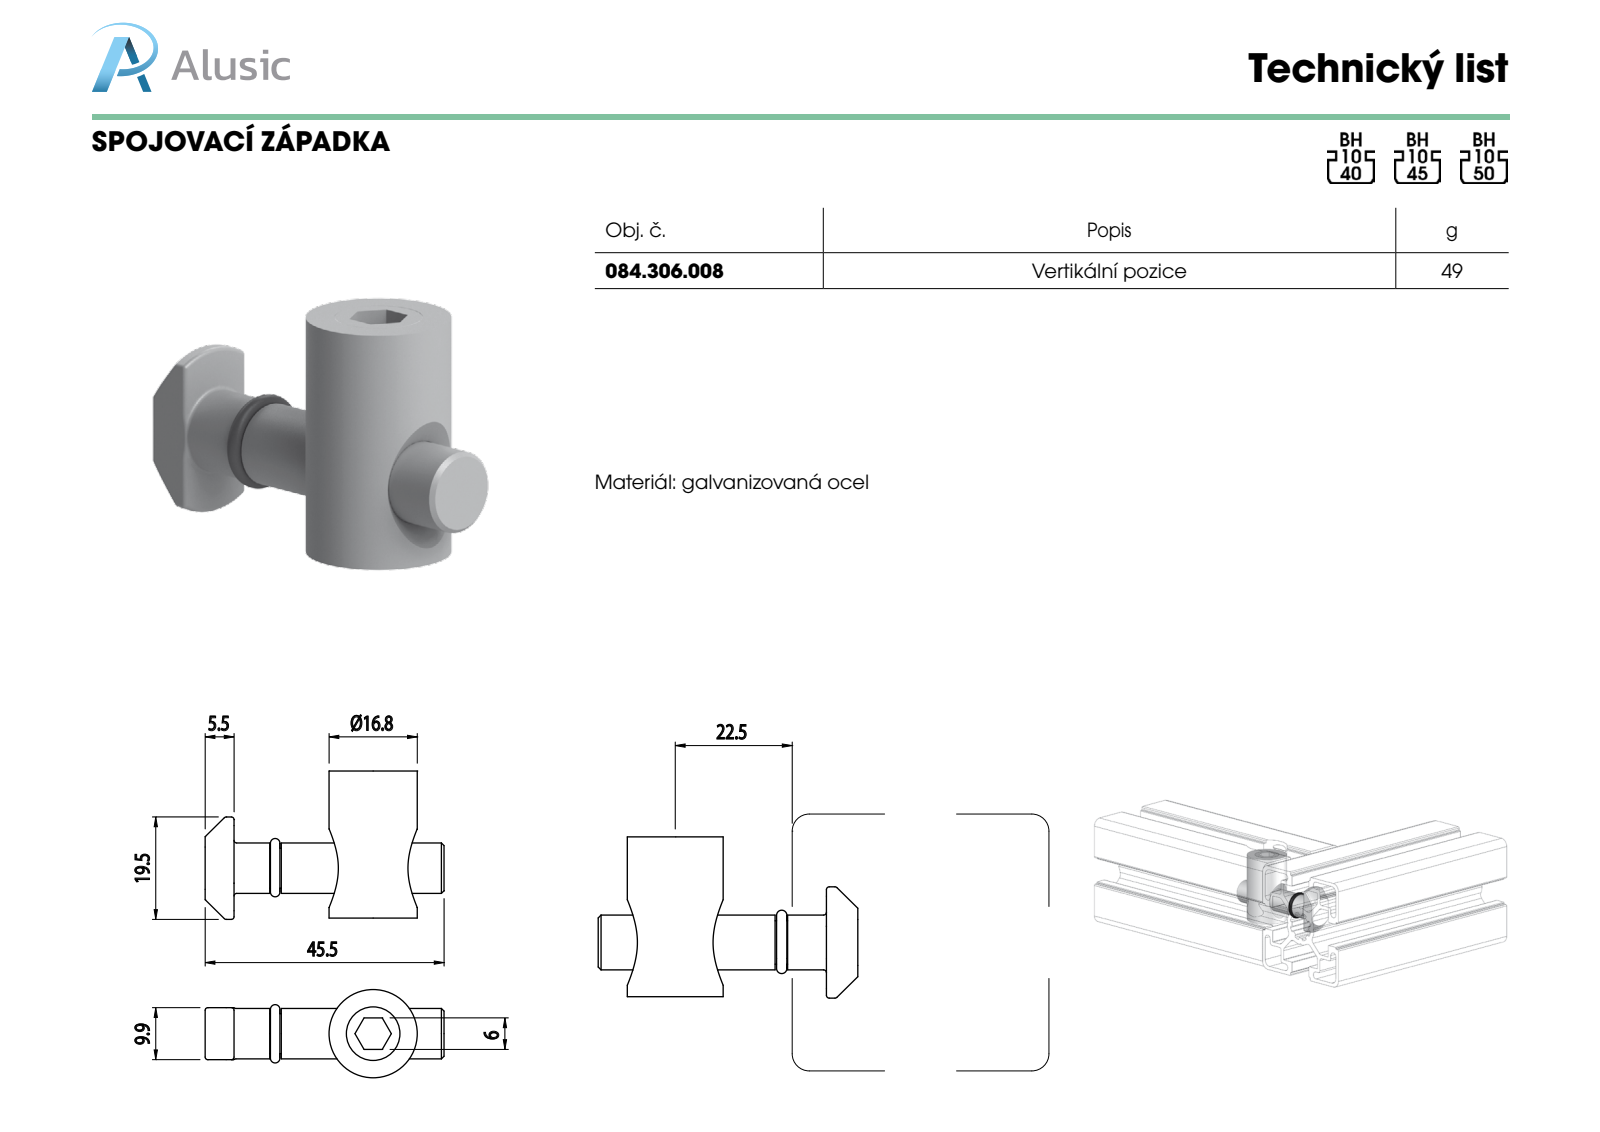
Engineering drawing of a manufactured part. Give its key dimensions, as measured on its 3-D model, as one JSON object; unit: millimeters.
{"part_name": "socket set screw cone point_iso_ISO 4027 - M12 x 16-C; o-rings series a_iso_O-ring 7.5x1.8-A-ISO 3601-1; 084.306.008; 084.306.008B (+1 more)", "step_written_by": "SolidWorks 2011 (CONFIG_CONTROL_DESIGN)", "units": "millimeters", "bodies": {"solids": 4, "faces": 95, "planar": 18, "cylindrical": 29, "other": 48}, "overall_size": [45.5, 28.25, 16.8], "volume_mm3": 8056, "surface_area_mm2": 5293, "round_holes": [[9.7, 1], [10.2, 1]], "round_bosses_or_shafts": [[16.8, 1], [12, 1], [9.6, 1], [7.6, 1]], "partial_cylinders_radius": [[0.5, 8], [9.75, 1]], "face_to_face_distances": [28, 6, 5.5, 9.9, 45.5, 40, 1.95, 7.95, 20, 8]}
